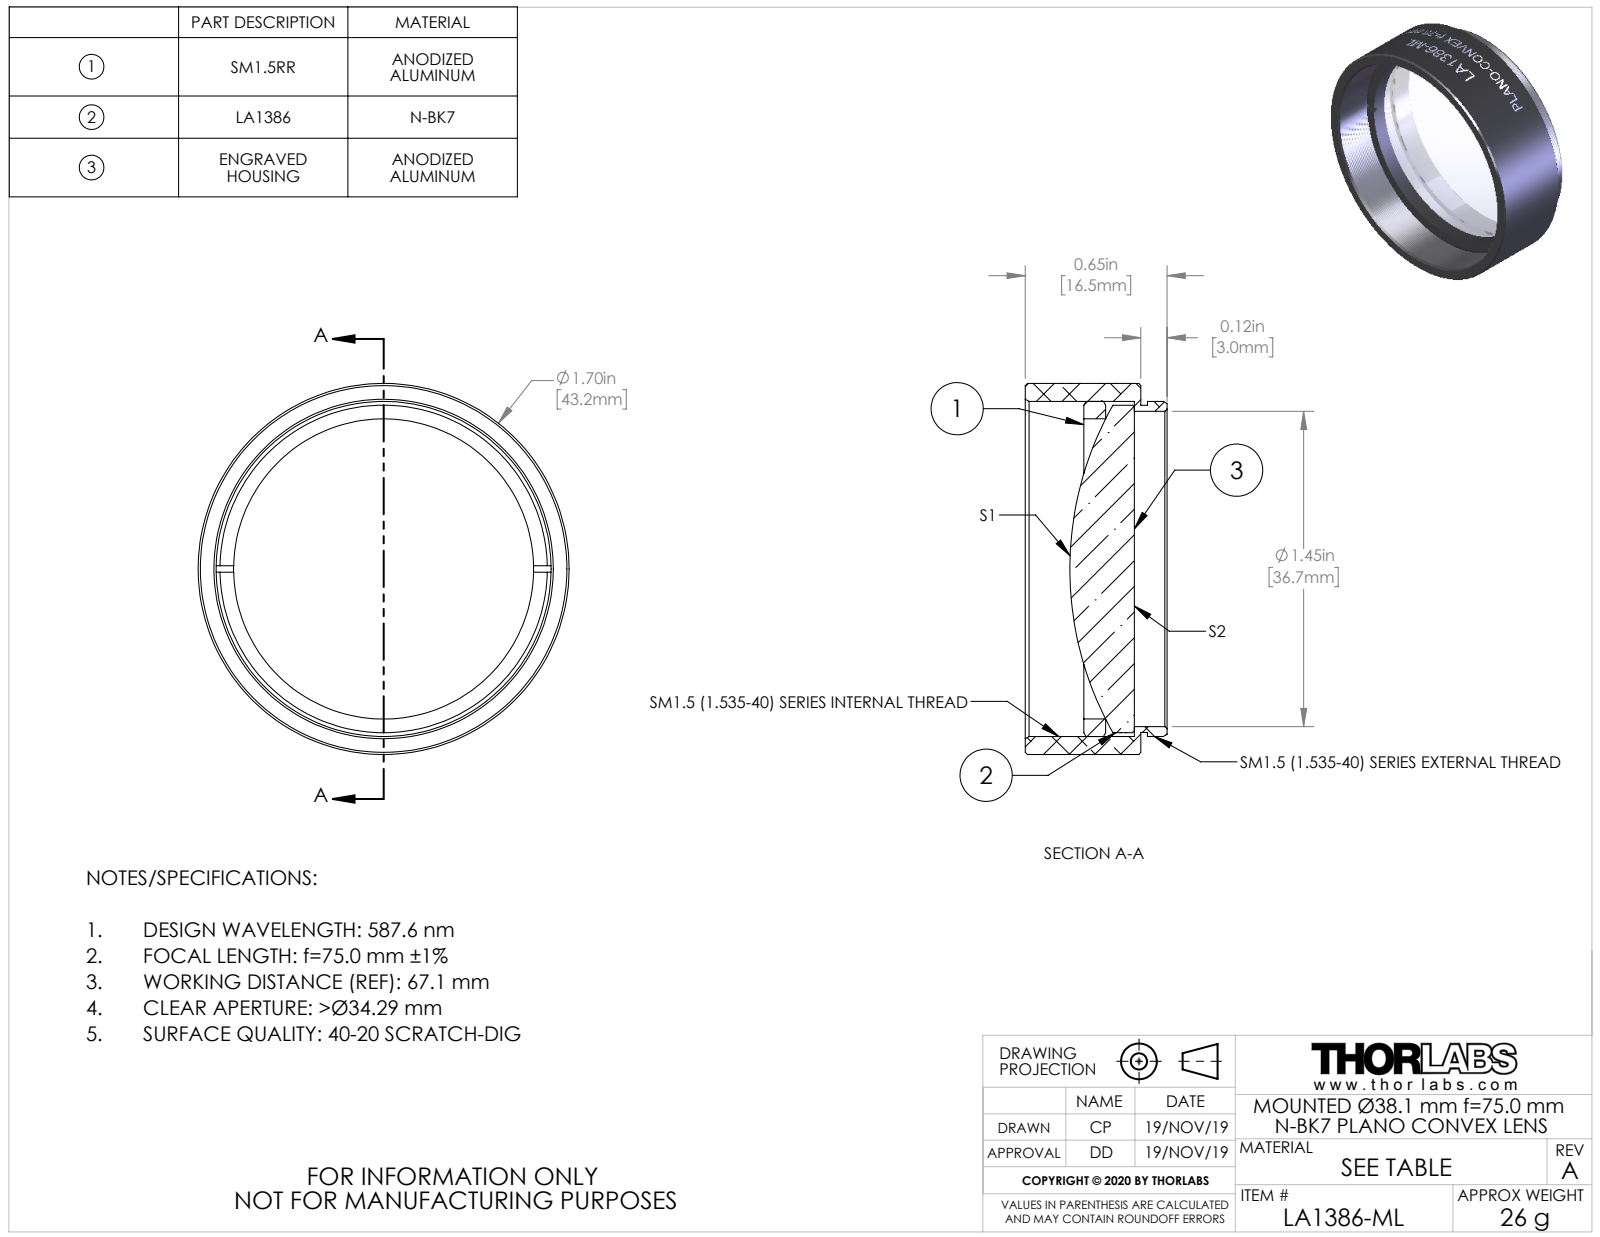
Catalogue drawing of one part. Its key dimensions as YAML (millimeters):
part_name: "TTN200686-E0W"
step_written_by: "SolidWorks 2018 (CONFIG_CONTROL_DESIGN)"
units: millimeters
bodies: {solids: 3, faces: 119, planar: 15, cylindrical: 85, other: 19}
overall_size: [43.18, 43.18, 16.51]
volume: 10435
surface_area: 8675
round_holes:
  - {diameter: 34.92, count: 1}
  - {diameter: 36.7, count: 1}
round_bosses_or_shafts:
  - {diameter: 43.18, count: 1}
  - {diameter: 38.99, count: 1}
  - {diameter: 38.1, count: 1}
  - {diameter: 38.07, count: 1}
face_to_face_distances: [0.76, 13.46, 12.7, 4.11, 3.35, 9.35, 6.65, 5.89, 2.54, 6.81]
